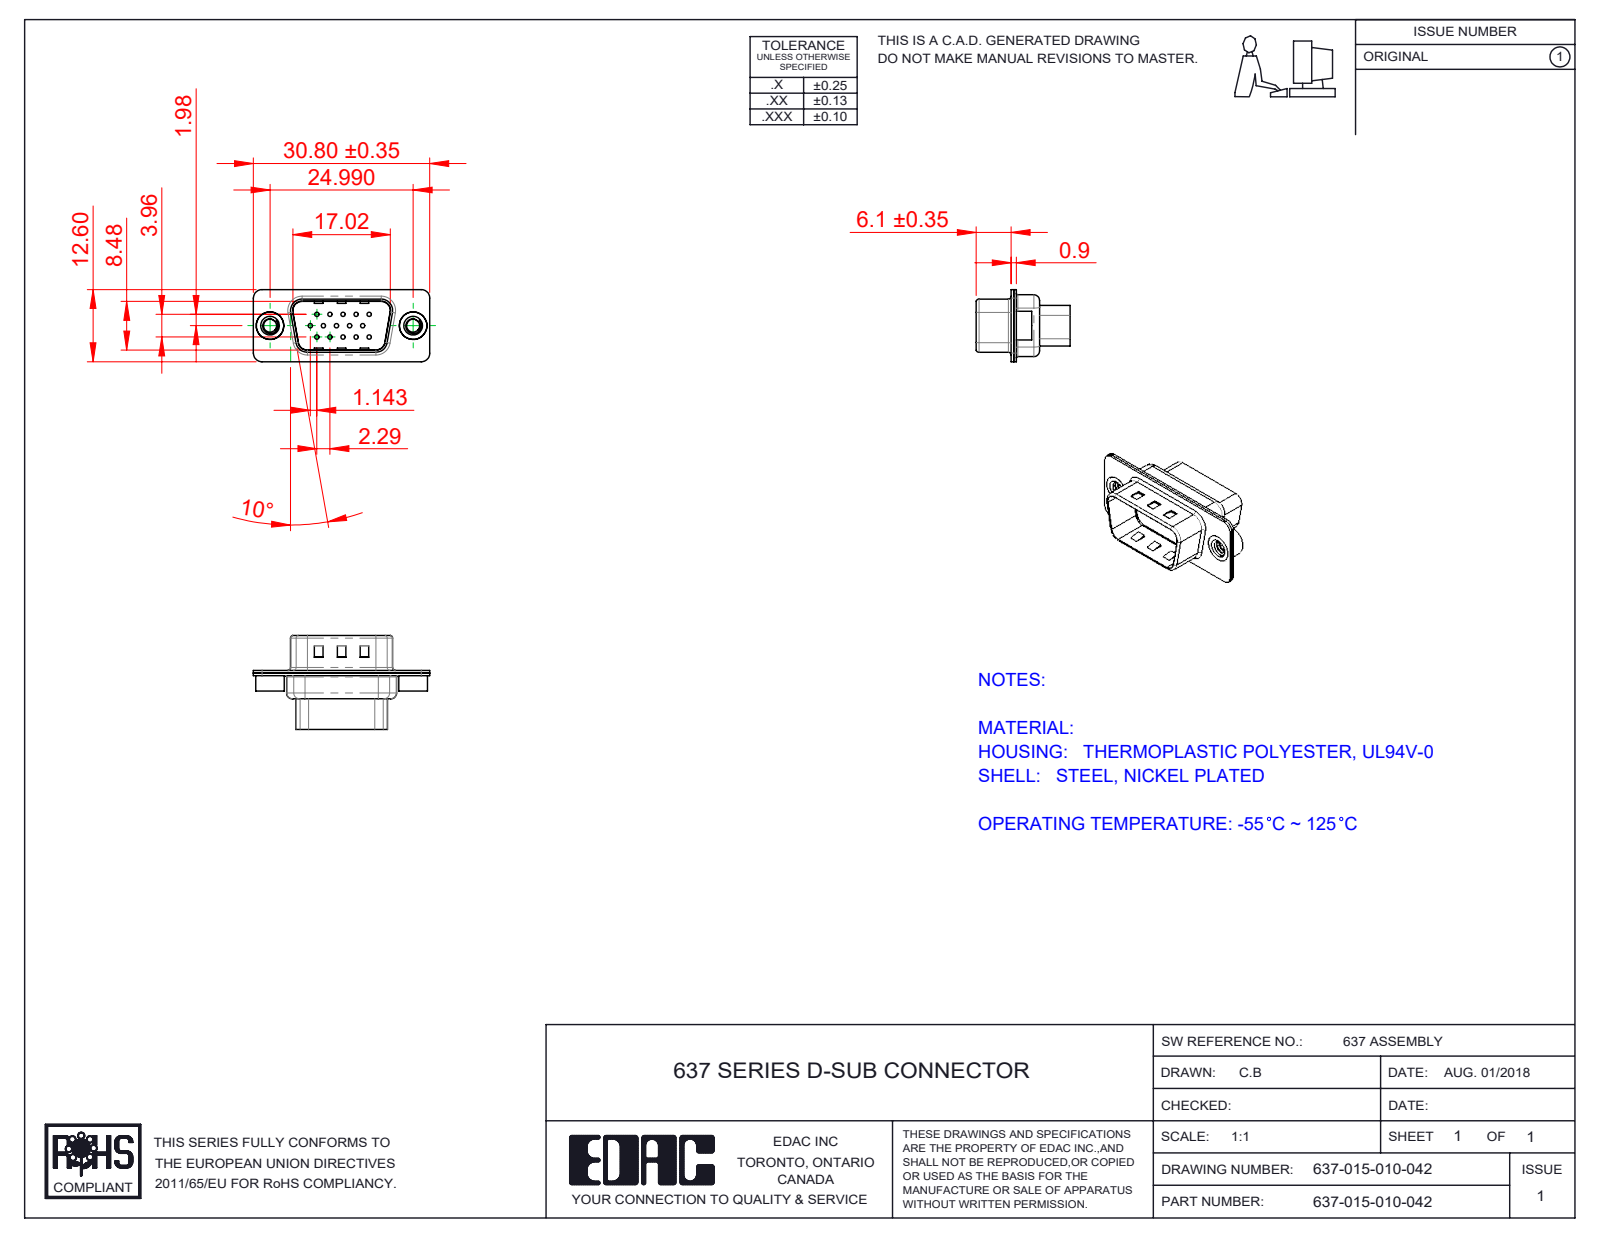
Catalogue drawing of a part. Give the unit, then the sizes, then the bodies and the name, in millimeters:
Units: millimetres
Overall size (bounding box): 30.8 × 16.4 × 12.6
Round holes (diameter × count): ⌀0.75 ×15, ⌀1.6 ×15, ⌀2 ×15, ⌀2.26 ×2, ⌀4 ×2, ⌀4.8 ×2
Round bosses / shafts (diameter × count): ⌀5 ×2, ⌀4.9 ×2
Partial cylindrical surfaces — rounded edges, fillets, slot ends (radius × count): R1.5 ×16, R2 ×12, R0.5 ×8, R0.25 ×4, R0.55 ×4, R0.7 ×4, R0.95 ×4, R1 ×4
Main face-to-face distances: 0.45, 0.9, 0.4, 0.7, 8.48, 7.78, 1.1, 8.18, 8.88, 1.35
Hole centre spacings: 3.96, 2.28, 4.57, 2.29, 6.05, 6.86, 7.92, 6.04
Volume: 1 487 mm³ · Surface area: 3 772 mm²
Bodies: 5 solids, 424 faces (137 planar, 219 cylindrical, 68 other)
Part name (STEP PRODUCT): 637 Shell Front_15 Contacts; 637 Housing_15 Contacts HP; 637 Shell Rear_15 Contacts; 637 4-40 Threaded Rivet (+1 more)
STEP written by: SolidWorks 2020 (CONFIG_CONTROL_DESIGN)
